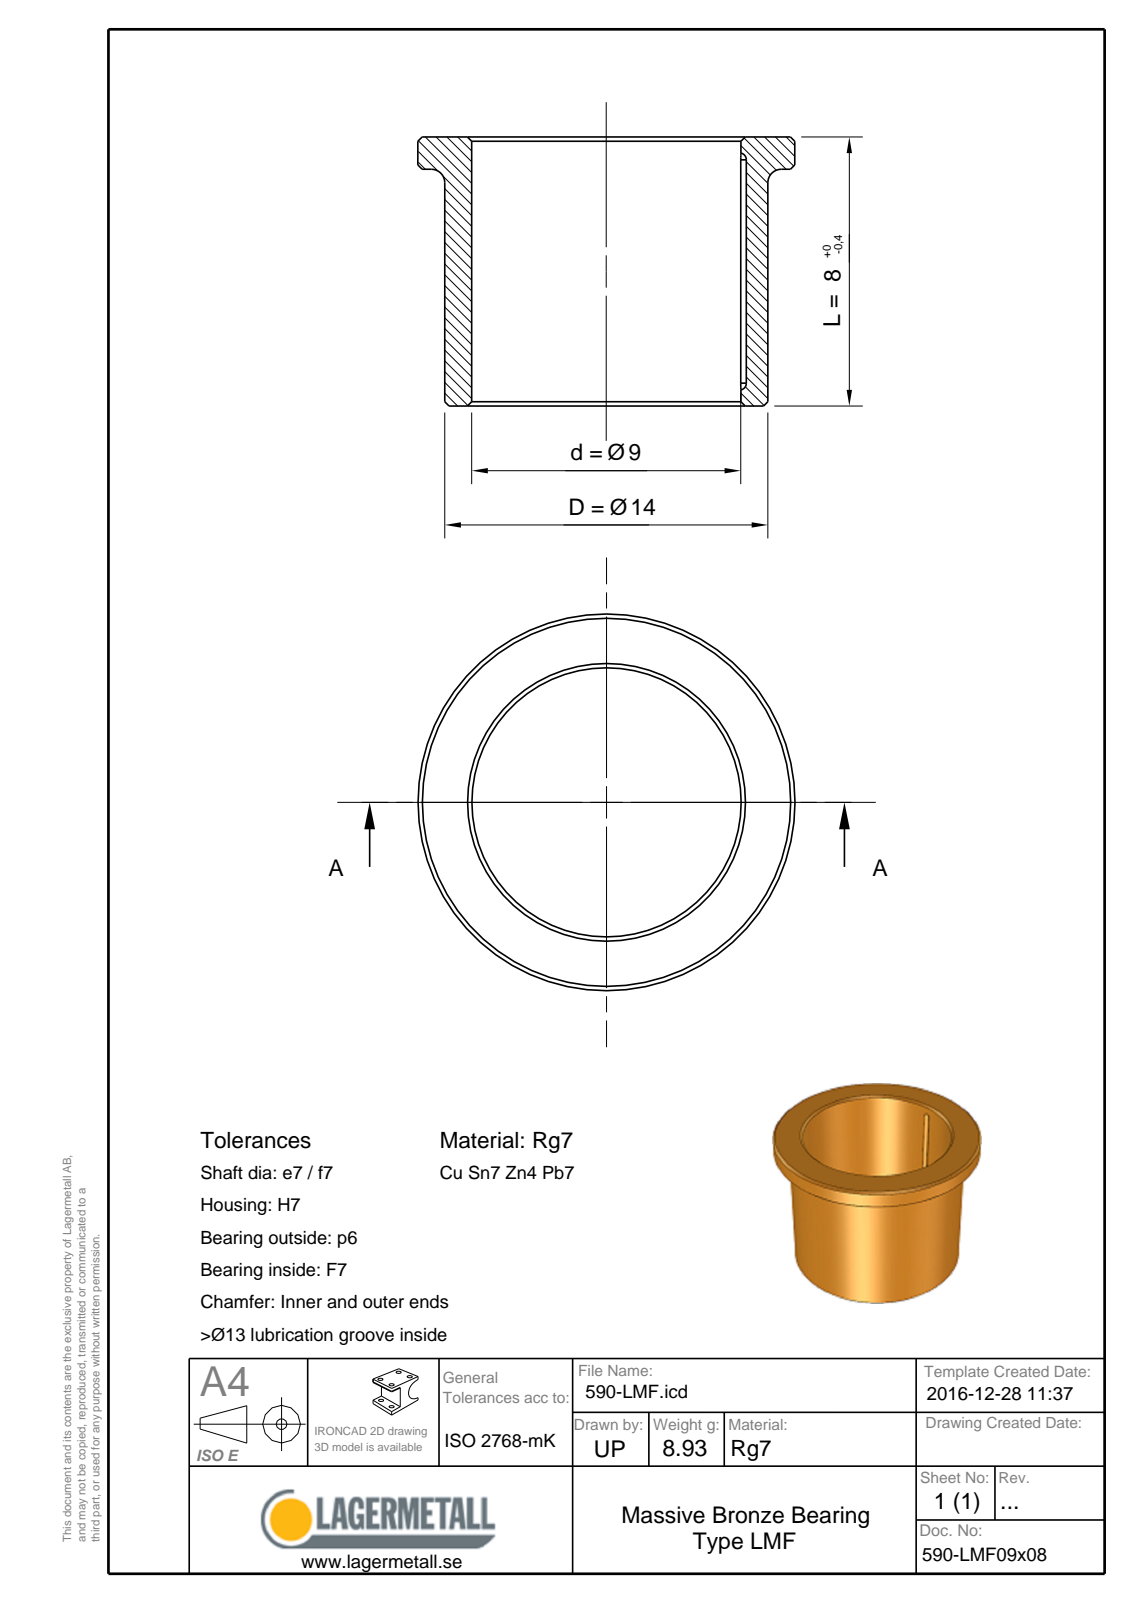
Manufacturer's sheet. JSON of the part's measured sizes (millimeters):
{"part_name": "590-LMF09x08", "step_written_by": "Spatial InterOp 3D (CONFIG_CONTROL_DESIGN)", "units": "millimeters", "bodies": {"solids": 1, "faces": 11, "planar": 3, "cylindrical": 3, "other": 5}, "overall_size": [18, 18, 8], "volume_mm3": 1015, "surface_area_mm2": 960, "round_holes": [[9, 1]], "round_bosses_or_shafts": [[18, 1], [14, 1]], "face_to_face_distances": [3, 5, 8]}
